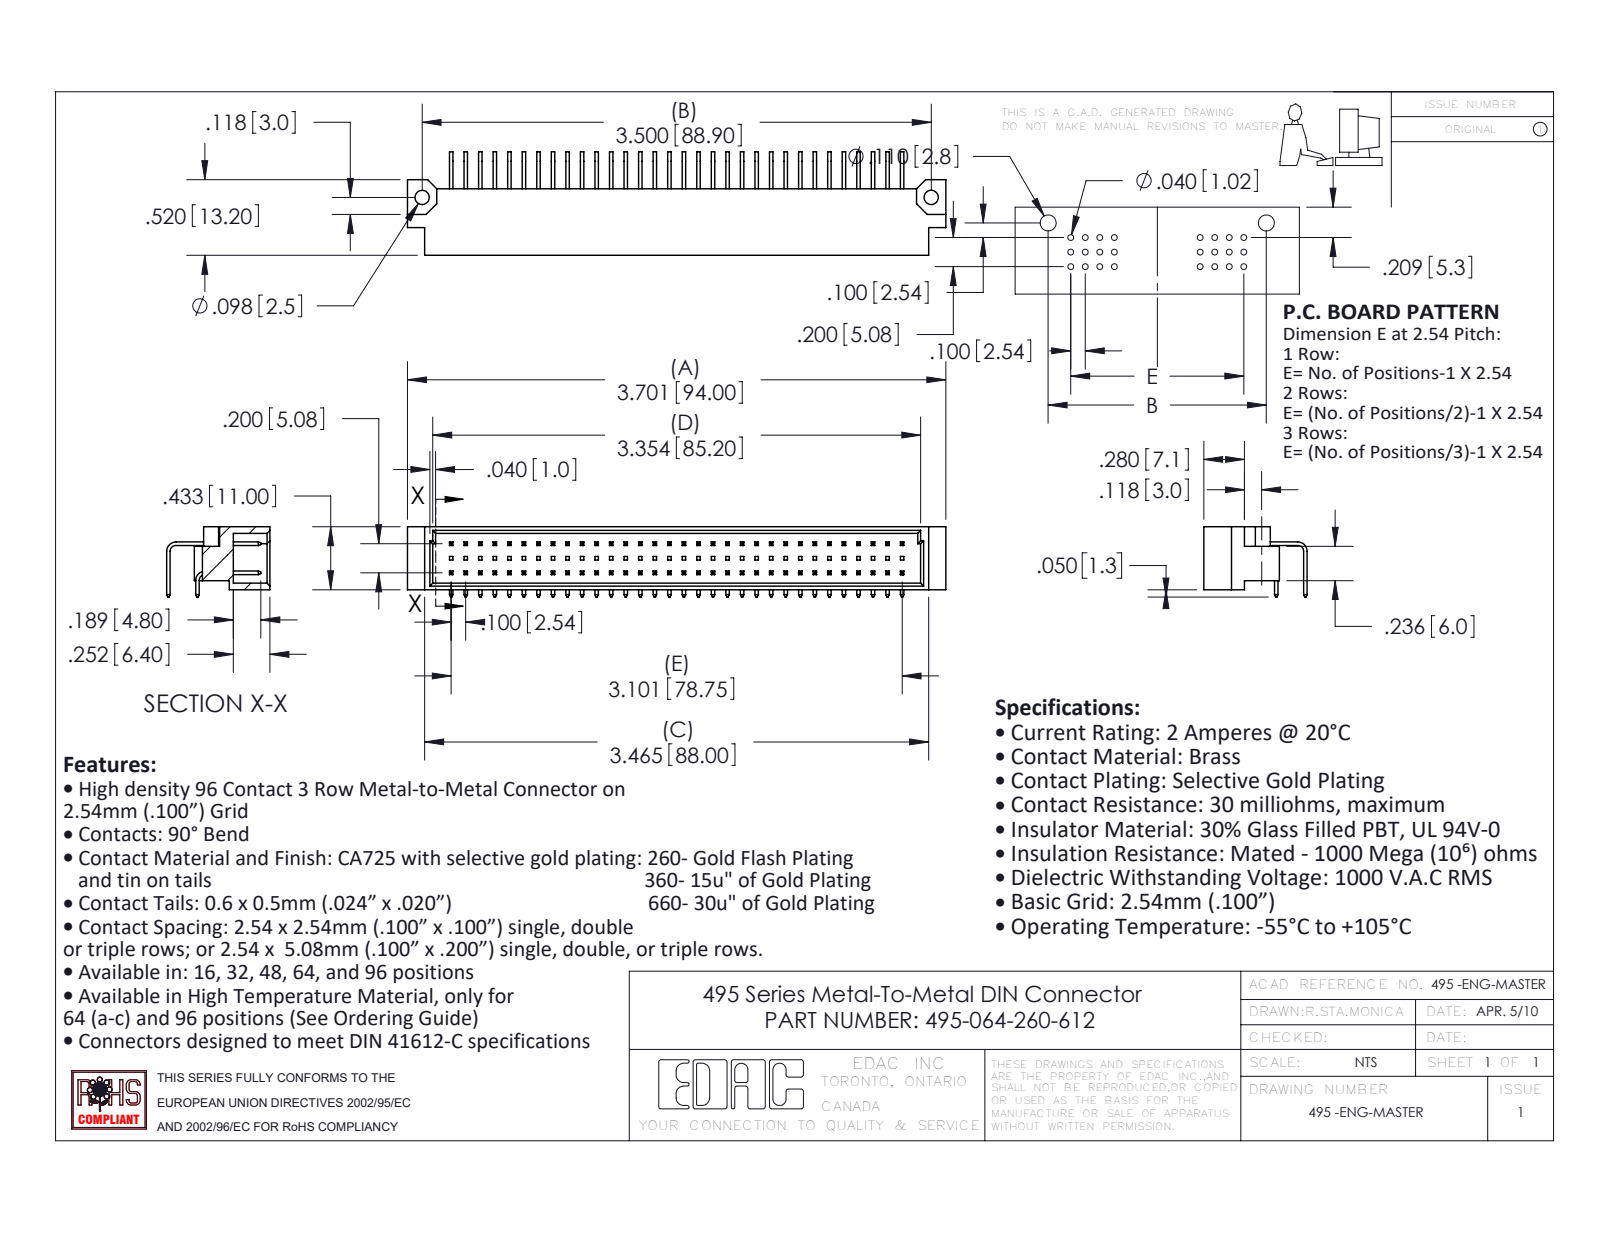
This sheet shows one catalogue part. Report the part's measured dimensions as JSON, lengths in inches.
{"part_name": "495-290-3; 495-064-260-612; 495 Part_96; 495-290-1", "step_written_by": "SolidWorks 2020 (AUTOMOTIVE_DESIGN)", "units": "inches", "bodies": {"solids": 65, "faces": 1585, "planar": 1453, "cylindrical": 132, "other": 0}, "overall_size": [3.701, 0.711, 0.483], "volume_in3": 0.39, "surface_area_in2": 15.36, "round_holes": [[0.098, 2]], "partial_cylinders_radius": [[0.04, 2], [0.065, 2]], "face_to_face_distances": [0.045, 0.388, 0.024, 0.2, 0.205, 0.433, 0.1, 0.343, 0.063, 0.37], "hole_center_spacings": [3.5]}
